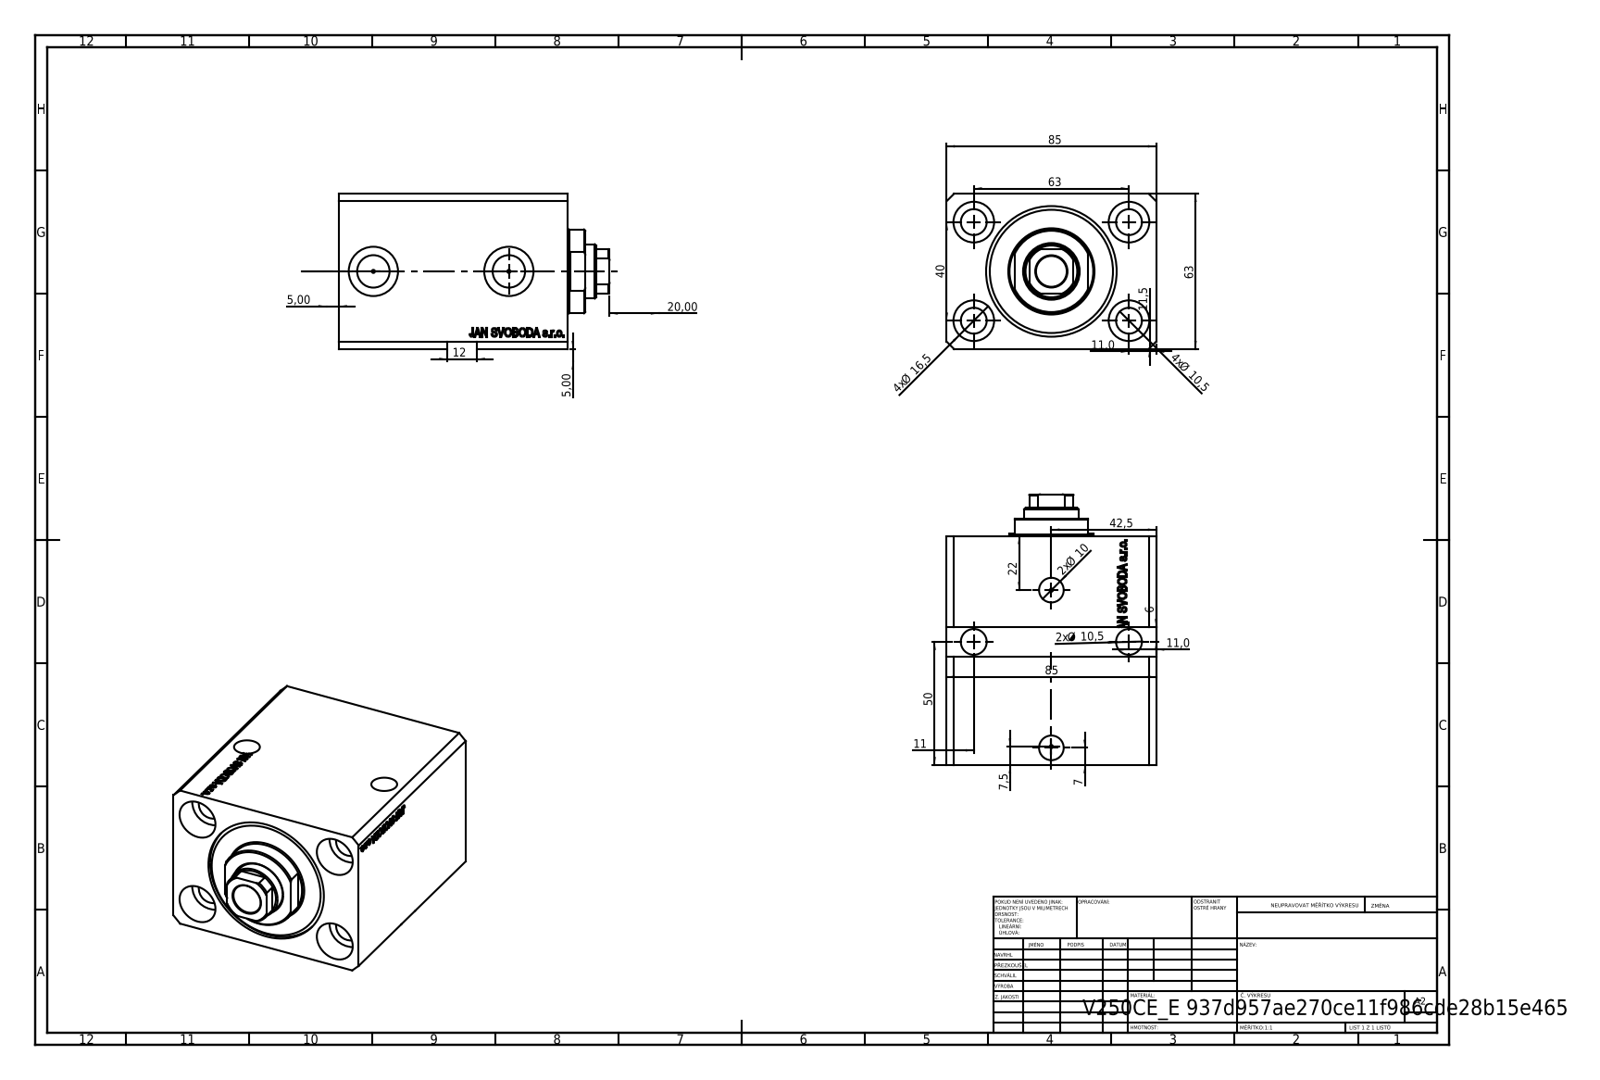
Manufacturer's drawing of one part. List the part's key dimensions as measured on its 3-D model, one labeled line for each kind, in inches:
Part name (STEP PRODUCT): V250CE_E_Body; V250CE_VC_E; V250CE_C_VCP
STEP written by: SolidWorks 2019 (CONFIG_CONTROL_DESIGN)
Units: inches
Bodies: 3 solids, 917 faces (459 planar, 84 cylindrical, 374 other)
Overall size (bounding box): 4.327 × 3.346 × 2.48
Volume: 26.07 in³ · Surface area: 138.6 in²
Round holes (diameter × count): ⌀0.413 ×6, ⌀0.049 ×4, ⌀0.65 ×4, ⌀0.394 ×2, ⌀0.518 ×2, ⌀0.787 ×2, ⌀0.492 ×1, ⌀0.866 ×1, ⌀1.575 ×1, ⌀2.087 ×1
Round bosses / shafts (diameter × count): ⌀1.339 ×1
Partial cylindrical surfaces — rounded edges, fillets, slot ends (radius × count): R0.413 ×1
Main face-to-face distances: 2.48, 3.346, 3.661, 2.594, 1.067, 0.449, 2.146, 3.213, 0.433, 3.228
Hole centre spacings: 1.469, 2.48, 1.491, 1.575, 2.082, 2.098, 2.938, 0.021
